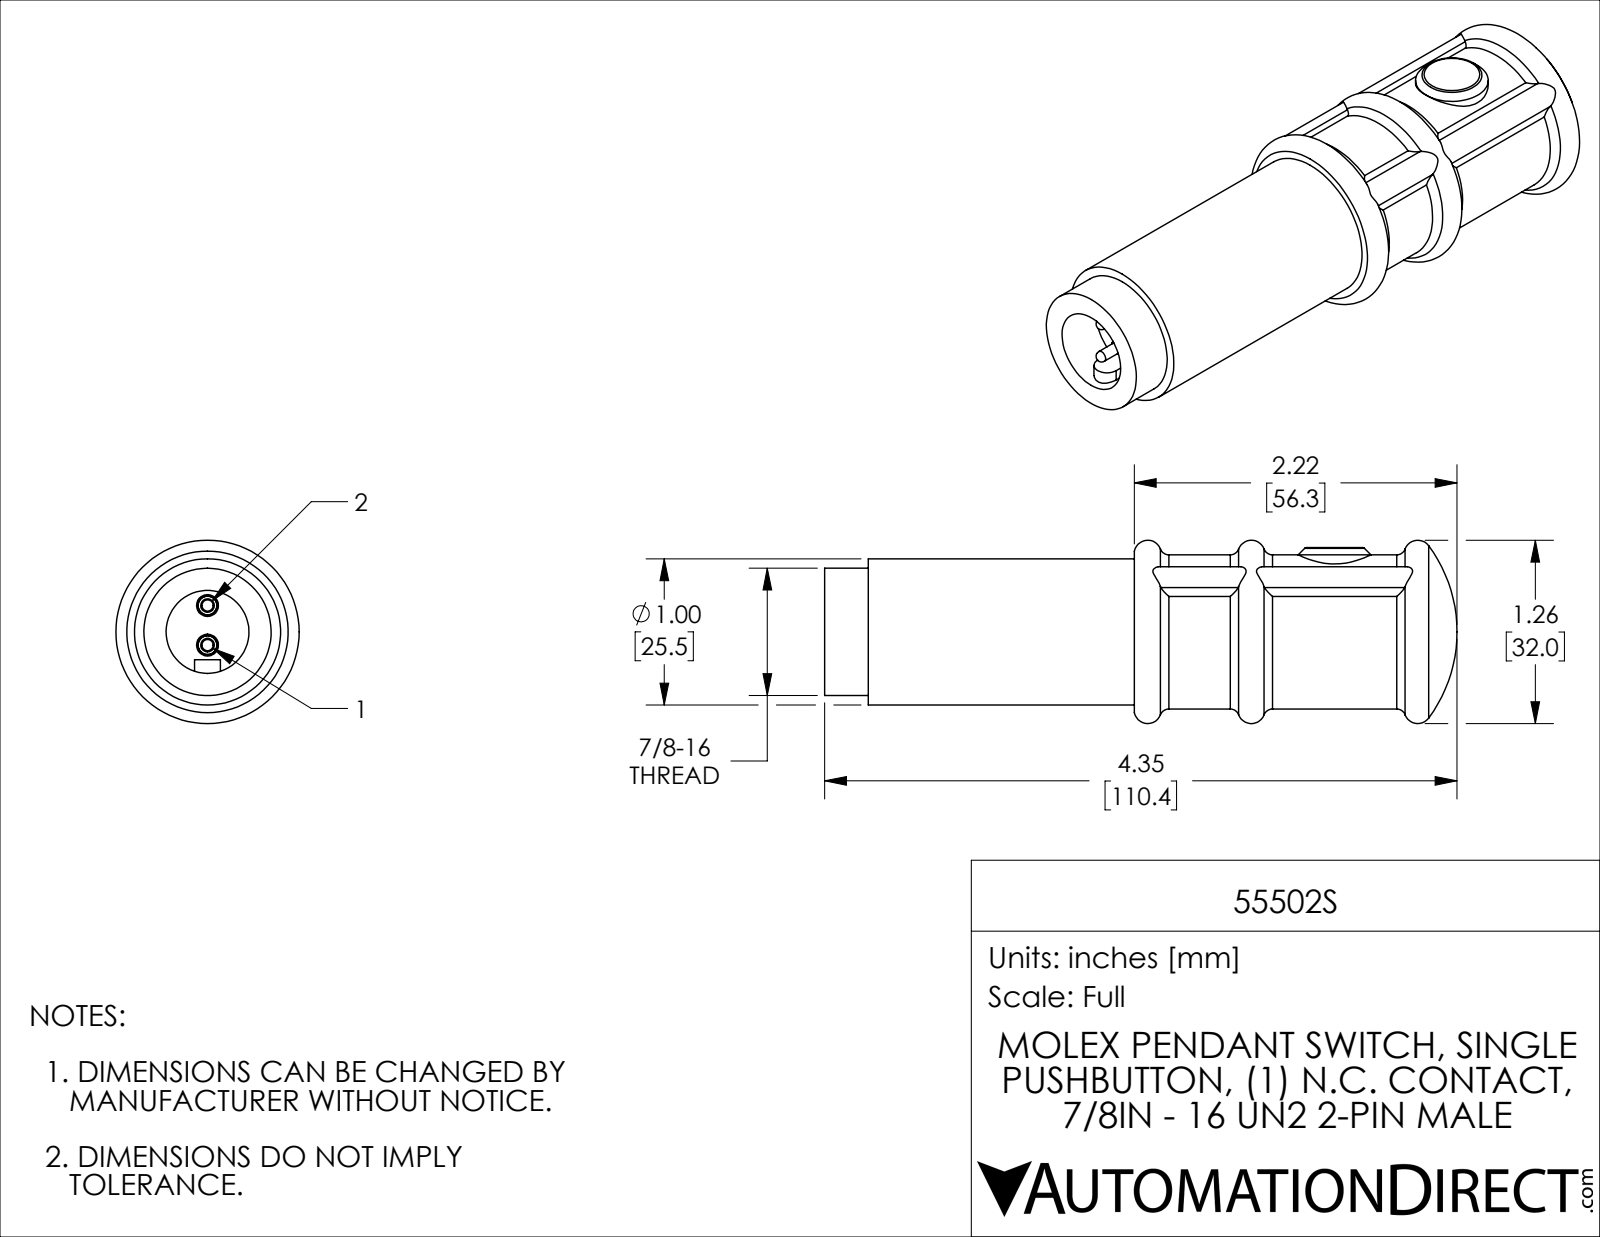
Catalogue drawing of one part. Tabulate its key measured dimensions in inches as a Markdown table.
| quantity | value |
| --- | --- |
| part name | 55502S |
| STEP written by | SolidWorks 2021 (CONFIG_CONTROL_DESIGN) |
| units | inches |
| bodies | 3 solids, 88 faces (12 planar, 38 cylindrical, 38 other) |
| overall size | 4.348 × 1.26 × 1.26 |
| volume | 3.659 in³ |
| surface area | 18.01 in² |
| round holes (diameter × count) | 0.57 × 1 |
| round bosses / shafts (diameter × count) | 0.077 × 2, 1.059 × 1, 1.005 × 1, 0.875 × 1, 0.5 × 1 |
| partial cylindrical surfaces (radius × count) | 0.062 × 4, 0.094 × 3, 0.089 × 1, 0.529 × 1 |
| main face-to-face distances | 0.333, 0.3, 0.033, 2.13, 1.83, 1.797, 0.771, 0.178, 0.243, 0.057 |
